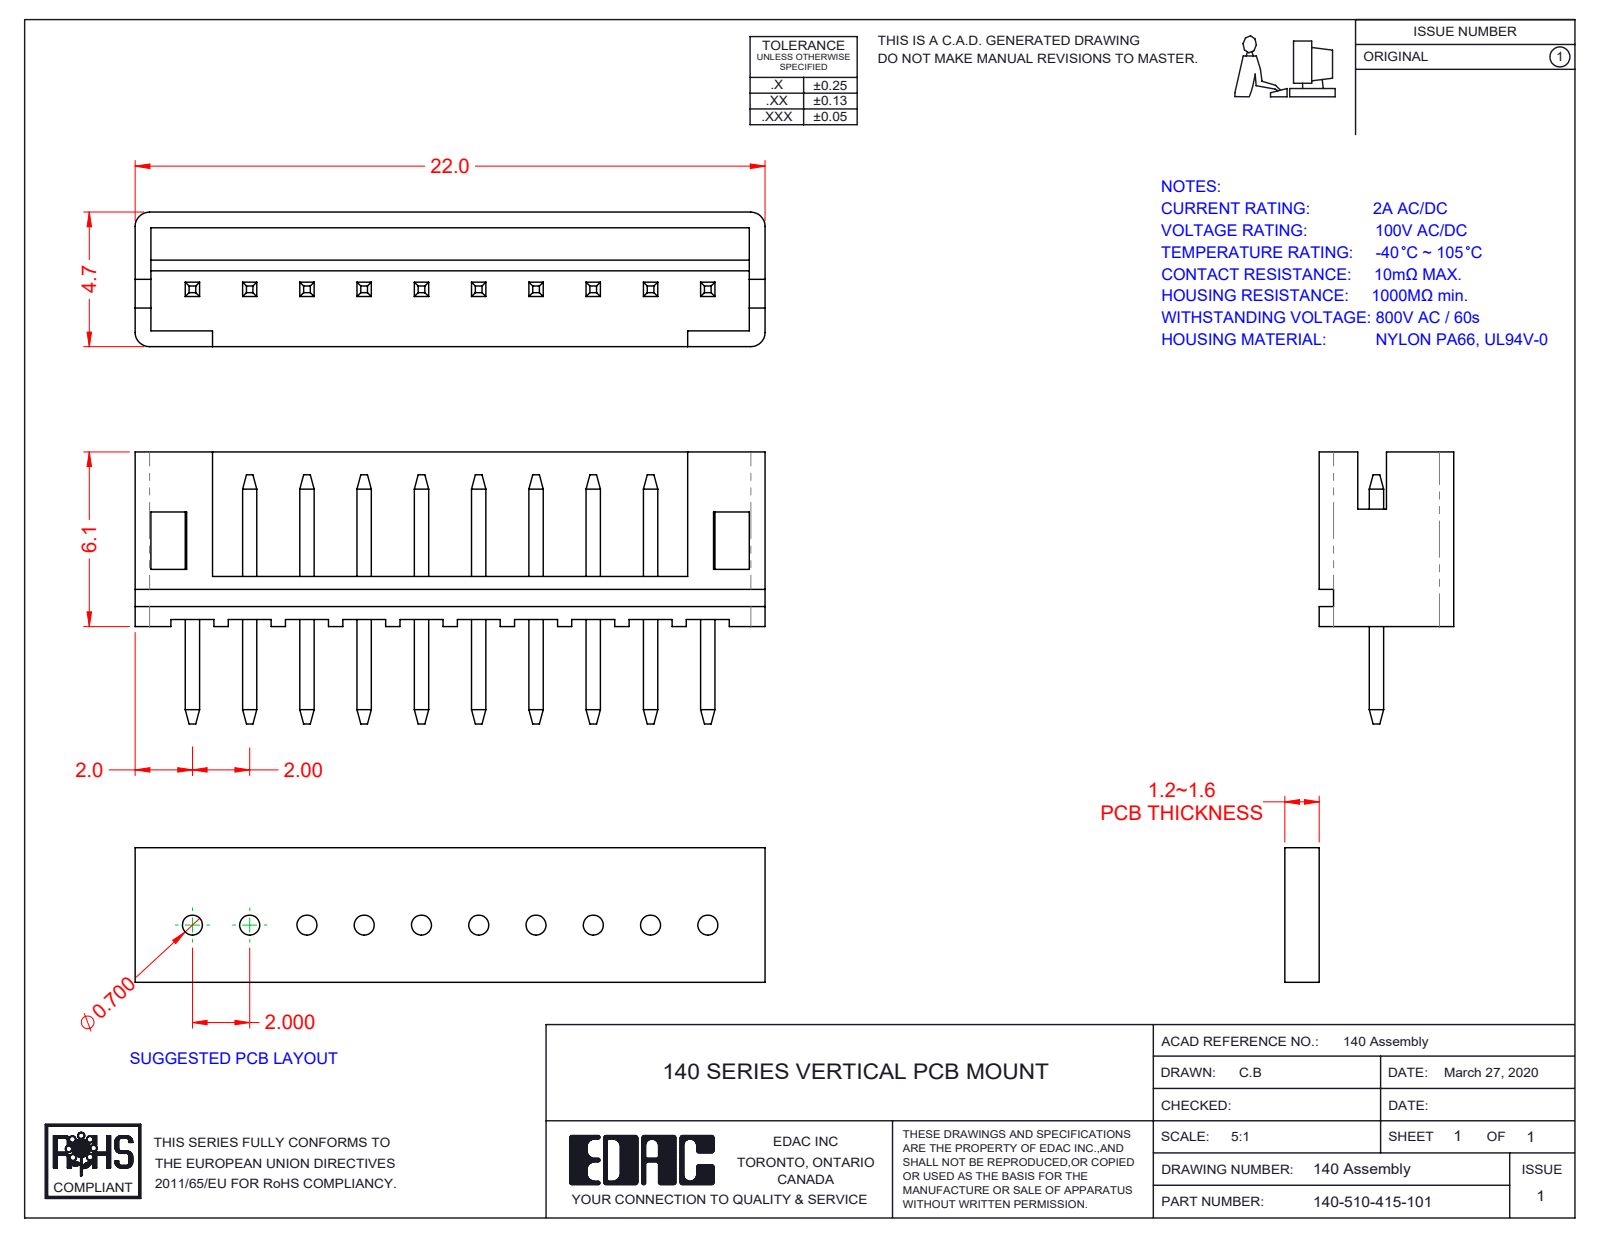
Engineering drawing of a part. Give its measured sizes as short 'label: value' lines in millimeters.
name: V LI Contact_Str; 140-510-415-101; V LI Housing_510
written by: SolidWorks 2020 (CONFIG_CONTROL_DESIGN)
unit: mm
bodies: 11 solids, 260 faces (254 planar, 6 cylindrical, 0 other)
size: 22 × 9.5 × 4.7
volume: 232 mm³; area: 850 mm²
rounds: 4× R0.5
face distances: 0.55, 0.5, 1.75, 1.5, 2, 4, 4.15, 2.45, 2.95, 1.9
